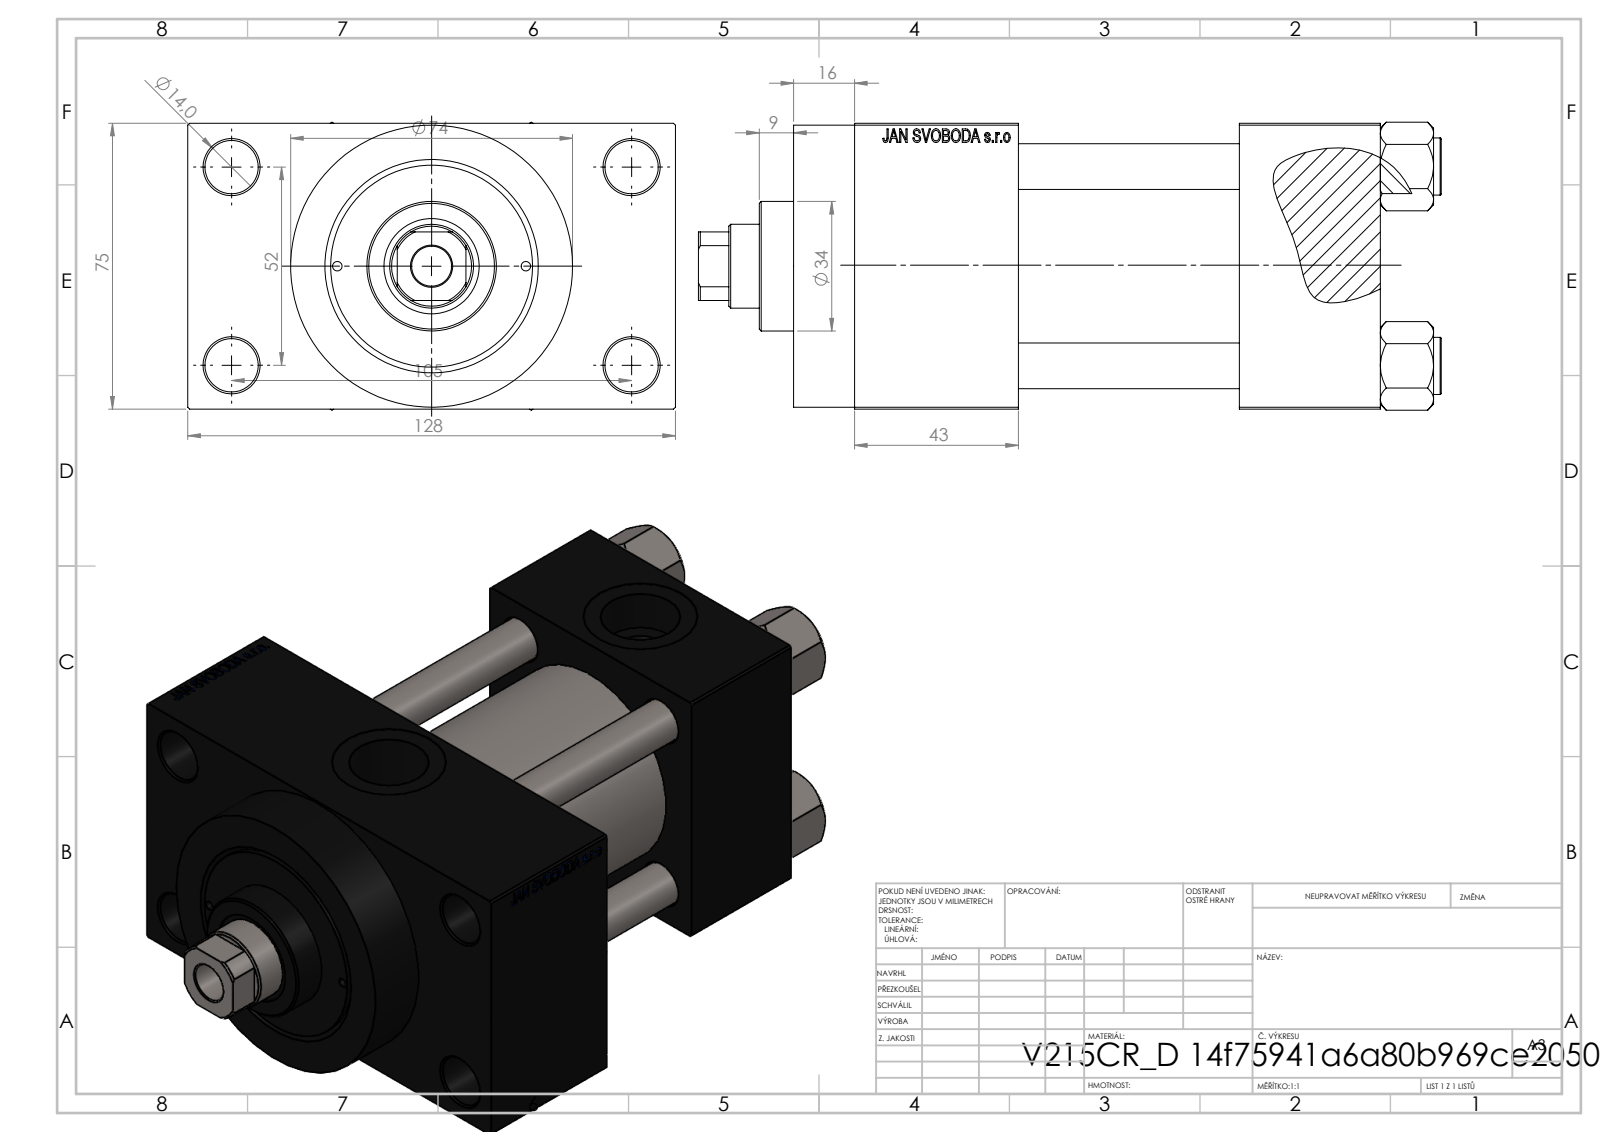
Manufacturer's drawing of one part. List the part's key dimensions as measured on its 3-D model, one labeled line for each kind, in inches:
Part name (STEP PRODUCT): V215_VC_A; NUT_M5_D; V215CR_D_Body; V215CR_D_TYCINKA (+1 more)
STEP written by: SolidWorks 2019 (CONFIG_CONTROL_DESIGN)
Units: inches
Bodies: 11 solids, 1112 faces (499 planar, 93 cylindrical, 520 other)
Overall size (bounding box): 7.677 × 5.039 × 2.974
Volume: 49.2 in³ · Surface area: 255.6 in²
Round holes (diameter × count): ⌀0.472 ×4, ⌀0.551 ×4, ⌀0.098 ×2, ⌀0.276 ×2, ⌀0.825 ×2, ⌀1.181 ×2, ⌀0.413 ×1, ⌀0.866 ×1, ⌀0.984 ×1, ⌀1.614 ×1, ⌀1.969 ×1, ⌀2.087 ×1
Round bosses / shafts (diameter × count): ⌀0.591 ×4, ⌀2.913 ×1, ⌀2.205 ×1, ⌀1.339 ×1
Partial cylindrical surfaces — rounded edges, fillets, slot ends (radius × count): R0.413 ×1
Main face-to-face distances: 2.953, 2.283, 1.457, 3.74, 1.043, 3.996, 5.433, 3.976, 1.693, 0.63
Hole centre spacings: 1.031, 1.037, 1.456, 1.497, 2.059, 2.253, 2.3, 2.307
